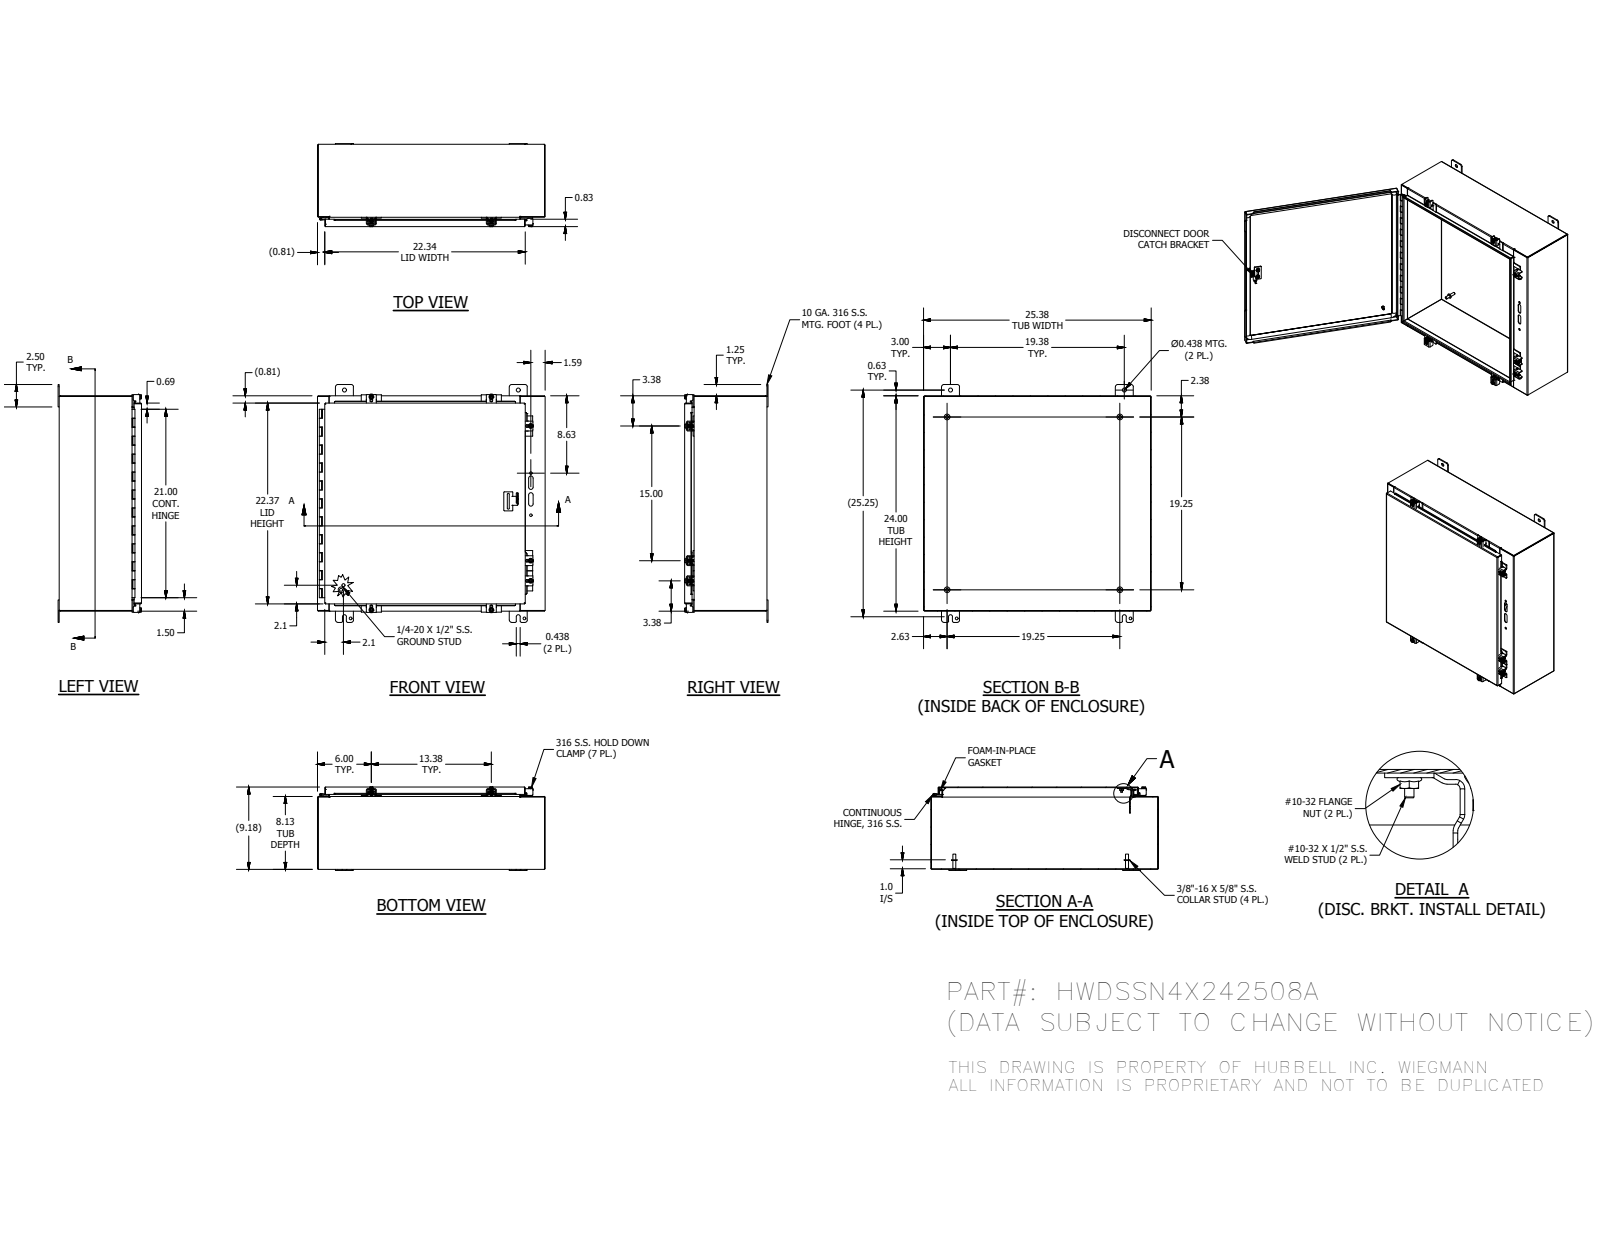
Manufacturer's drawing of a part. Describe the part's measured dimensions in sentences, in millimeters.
The part is named "SSN4X242508ABKP; 38859; 34839; 32874-24T (+8 more)". Its 3-D file was written by "Autodesk Inventor 2016 (AUTOMOTIVE_DESIGN)". It is 20 solids with 754 faces: 445 planar, 227 cylindrical and 82 other. Overall it measures 673.1 by 644.52 by 236.25 millimeters. Its volume is 2 996 000 cubic millimeters and its surface area 3 041 000 square millimeters. Round holes: 4 of diameter 7.95, 4 of diameter 11.13, 2 of diameter 3.17, 2 of diameter 3.96, 2 of diameter 7.14. Round bosses or shafts: 4 of diameter 15.88, 4 of diameter 8.38, 3 of diameter 8.56, 2 of diameter 6.35, 2 of diameter 4.83, 1 of diameter 3.05. Partial cylindrical surfaces (rounded edges, fillets, slot ends): 27 of radius 0.79, 23 of radius 2.67, 21 of radius 6.35, 11 of radius 3.17, 8 of radius 0.25, 8 of radius 1.92, 5 of radius 2.38, 5 of radius 4.76. The main face-to-face distances are 1.88, 231.19, 229.31, 233.07, 607.72, 1.87, 204.5, 26.69, 609.6, 605.84. The hole center spacings are 609.6, 40.45, 492.12, 783.45, 510.87, 573.38, 646.33, 28.58.
